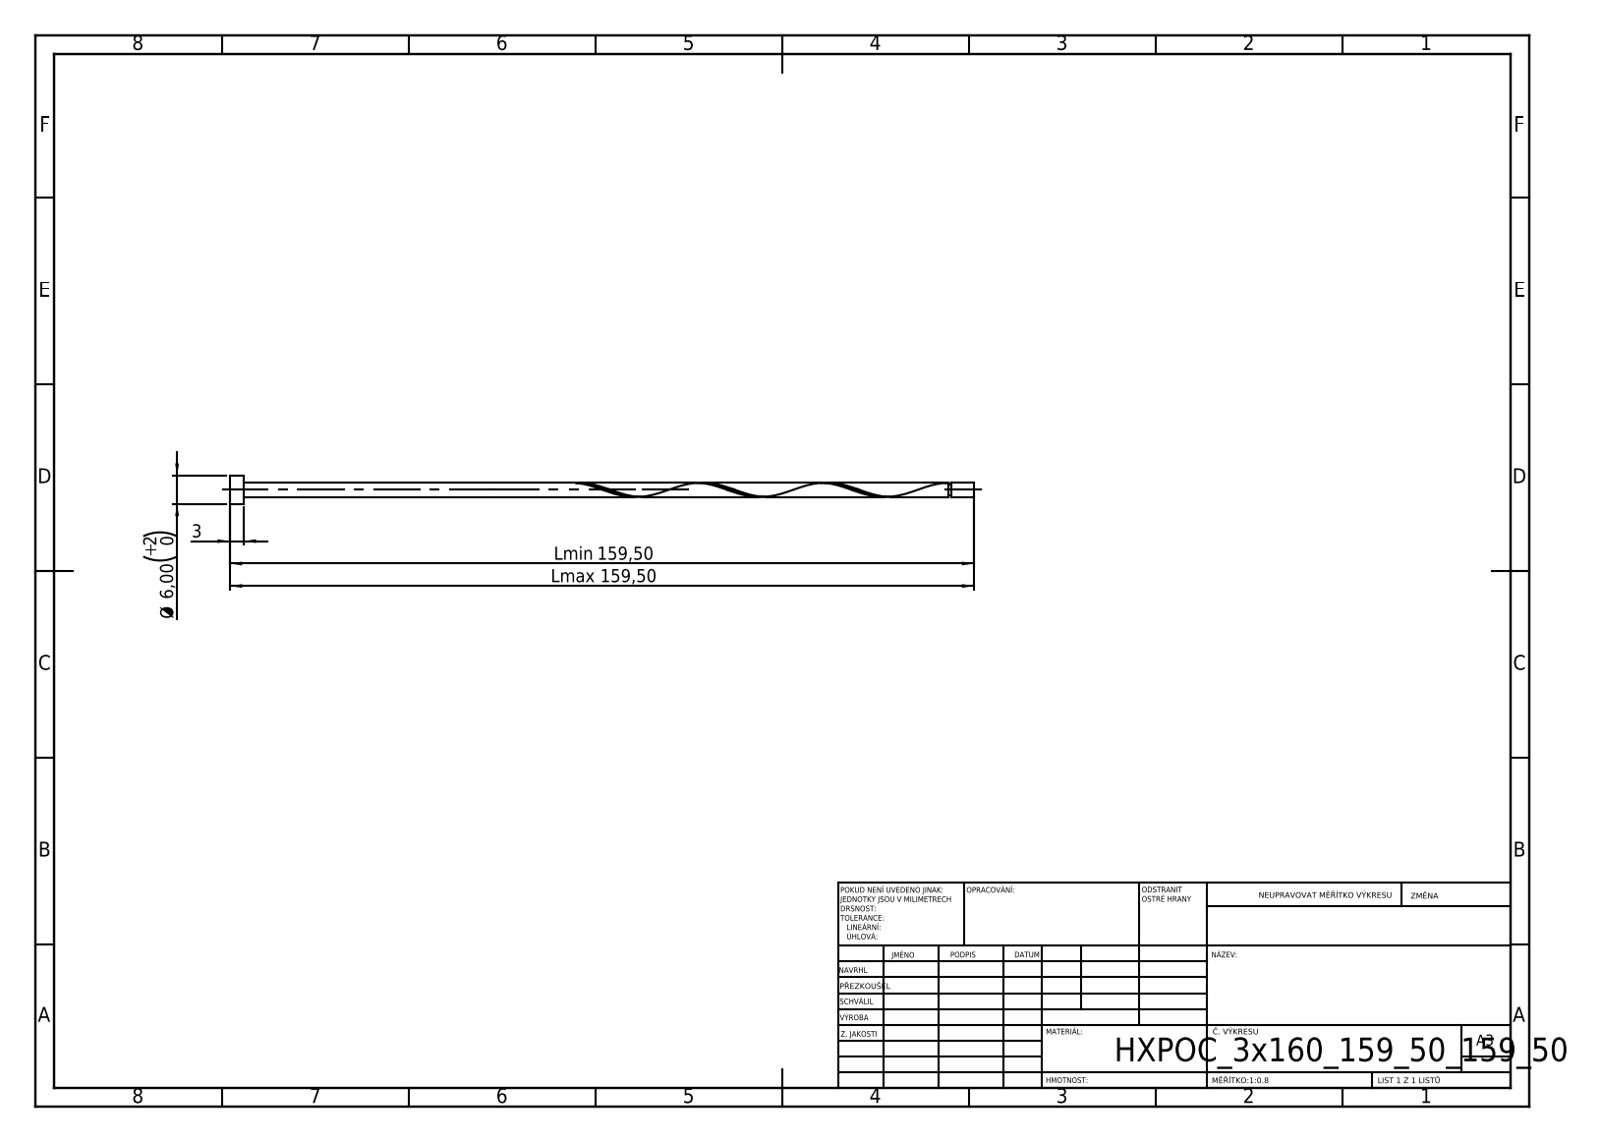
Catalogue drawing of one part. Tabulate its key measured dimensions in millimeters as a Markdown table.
| quantity | value |
| --- | --- |
| STEP written by | SolidWorks 2019 (CONFIG_CONTROL_DESIGN) |
| units | millimeters |
| bodies | 1 solid, 16 faces (6 planar, 9 cylindrical, 1 other) |
| overall size | 159.5 × 6 × 6 |
| volume | 1 430 mm³ |
| surface area | 2 119 mm² |
| round bosses / shafts (diameter × count) | 6 × 1, 3 × 1, 2.4 × 1 |
| main face-to-face distances | 3, 159.5, 156.5, 154.64, 151.64, 4.86, 154.04, 151.04, 0.6, 5.46 |
